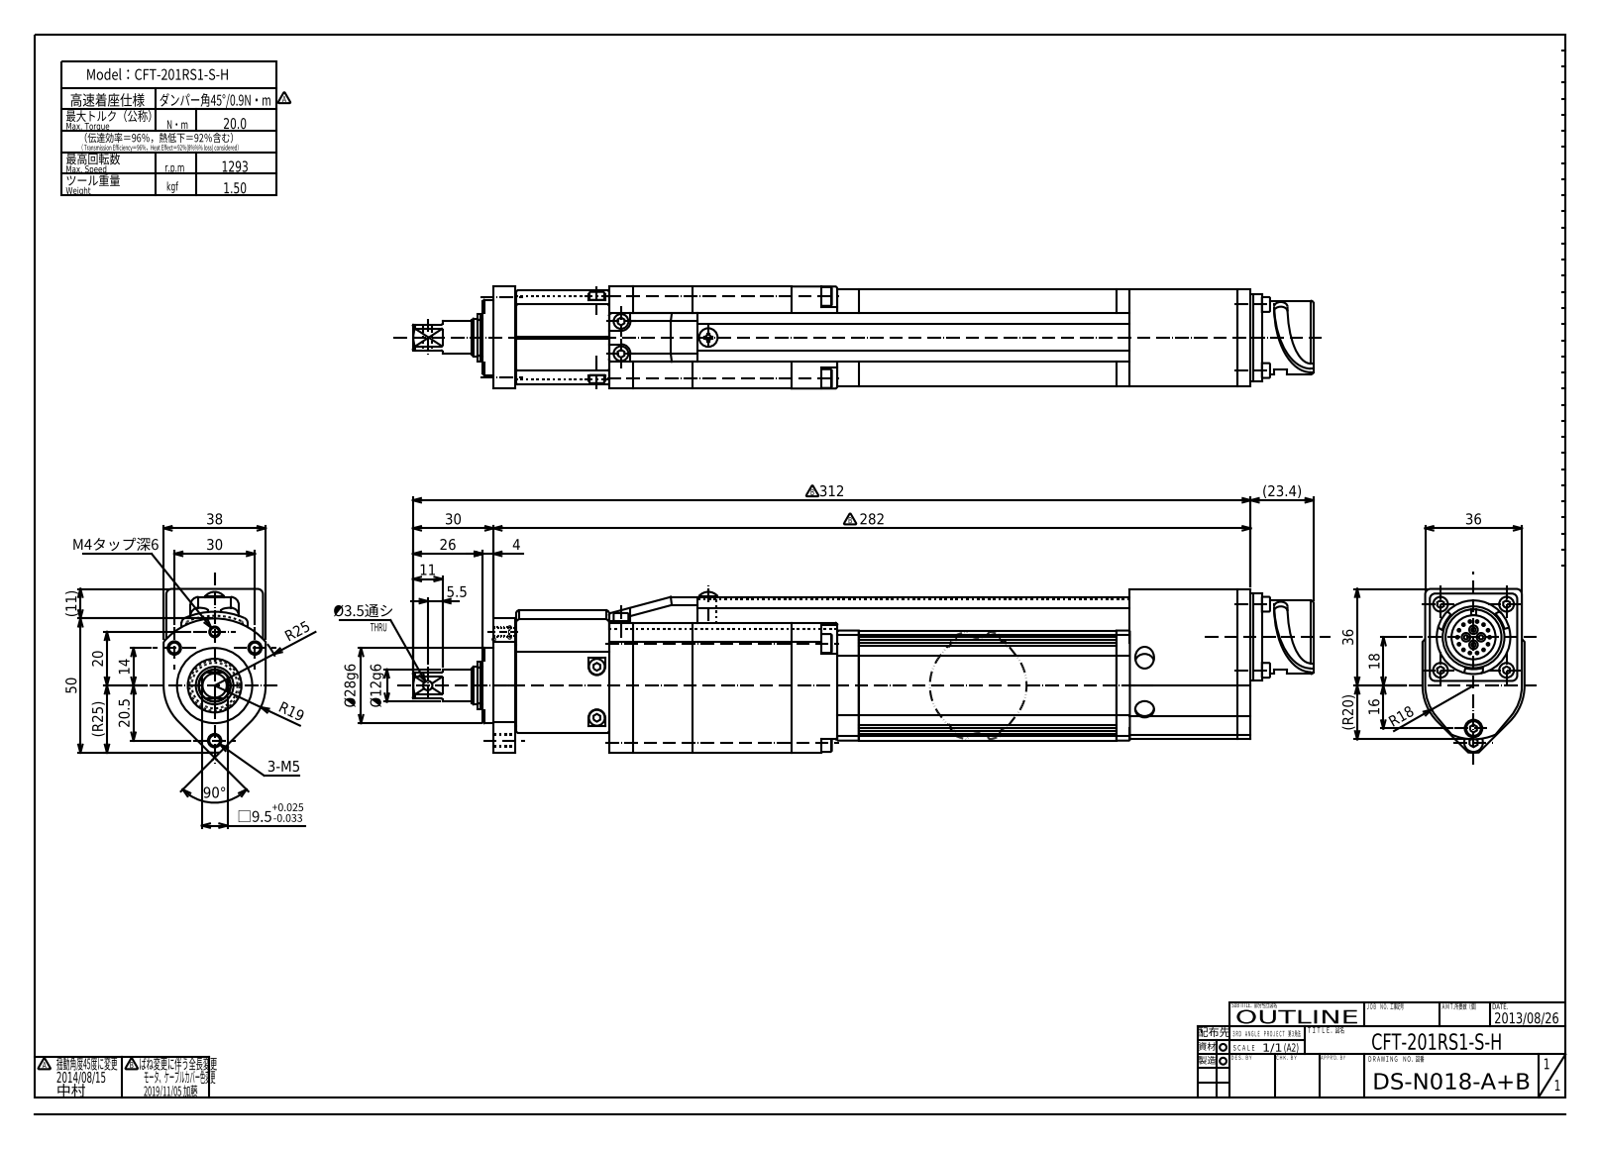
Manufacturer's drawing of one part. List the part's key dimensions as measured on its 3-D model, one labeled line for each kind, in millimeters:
Part name (STEP PRODUCT): CFT-201RS1-S-H(DS-N018-C+F)_OUTLINE_20201118
STEP written by: Autodesk Inventor 2021 (AUTOMOTIVE_DESIGN)
Units: millimetres
Bodies: 1 solid, 707 faces (436 planar, 195 cylindrical, 76 other)
Overall size (bounding box): 335.4 × 61 × 38
Volume: 430 847 mm³ · Surface area: 63 231 mm²
Round holes (diameter × count): ⌀4.13 ×3, ⌀1.2 ×2, ⌀7 ×2, ⌀3.24 ×1, ⌀3.5 ×1, ⌀6.5 ×1, ⌀14.7 ×1, ⌀20 ×1, ⌀20.8 ×1, ⌀31 ×1
Round bosses / shafts (diameter × count): ⌀1 ×14, ⌀5.5 ×13, ⌀4.5 ×4, ⌀1.6 ×4, ⌀7 ×3, ⌀4 ×3, ⌀6 ×2, ⌀28 ×1
Partial cylindrical surfaces — rounded edges, fillets, slot ends (radius × count): R0.3 ×8, R3 ×7, R2 ×6, R4 ×5, R0.5 ×4, R2.75 ×4, R3.25 ×4, R1 ×3
Main face-to-face distances: 1, 27, 10, 9, 28, 37, 36, 3, 12.5, 18
Hole centre spacings: 7.76, 10.7, 12.67, 14.53, 15.52, 16.16, 18.21, 20.52
